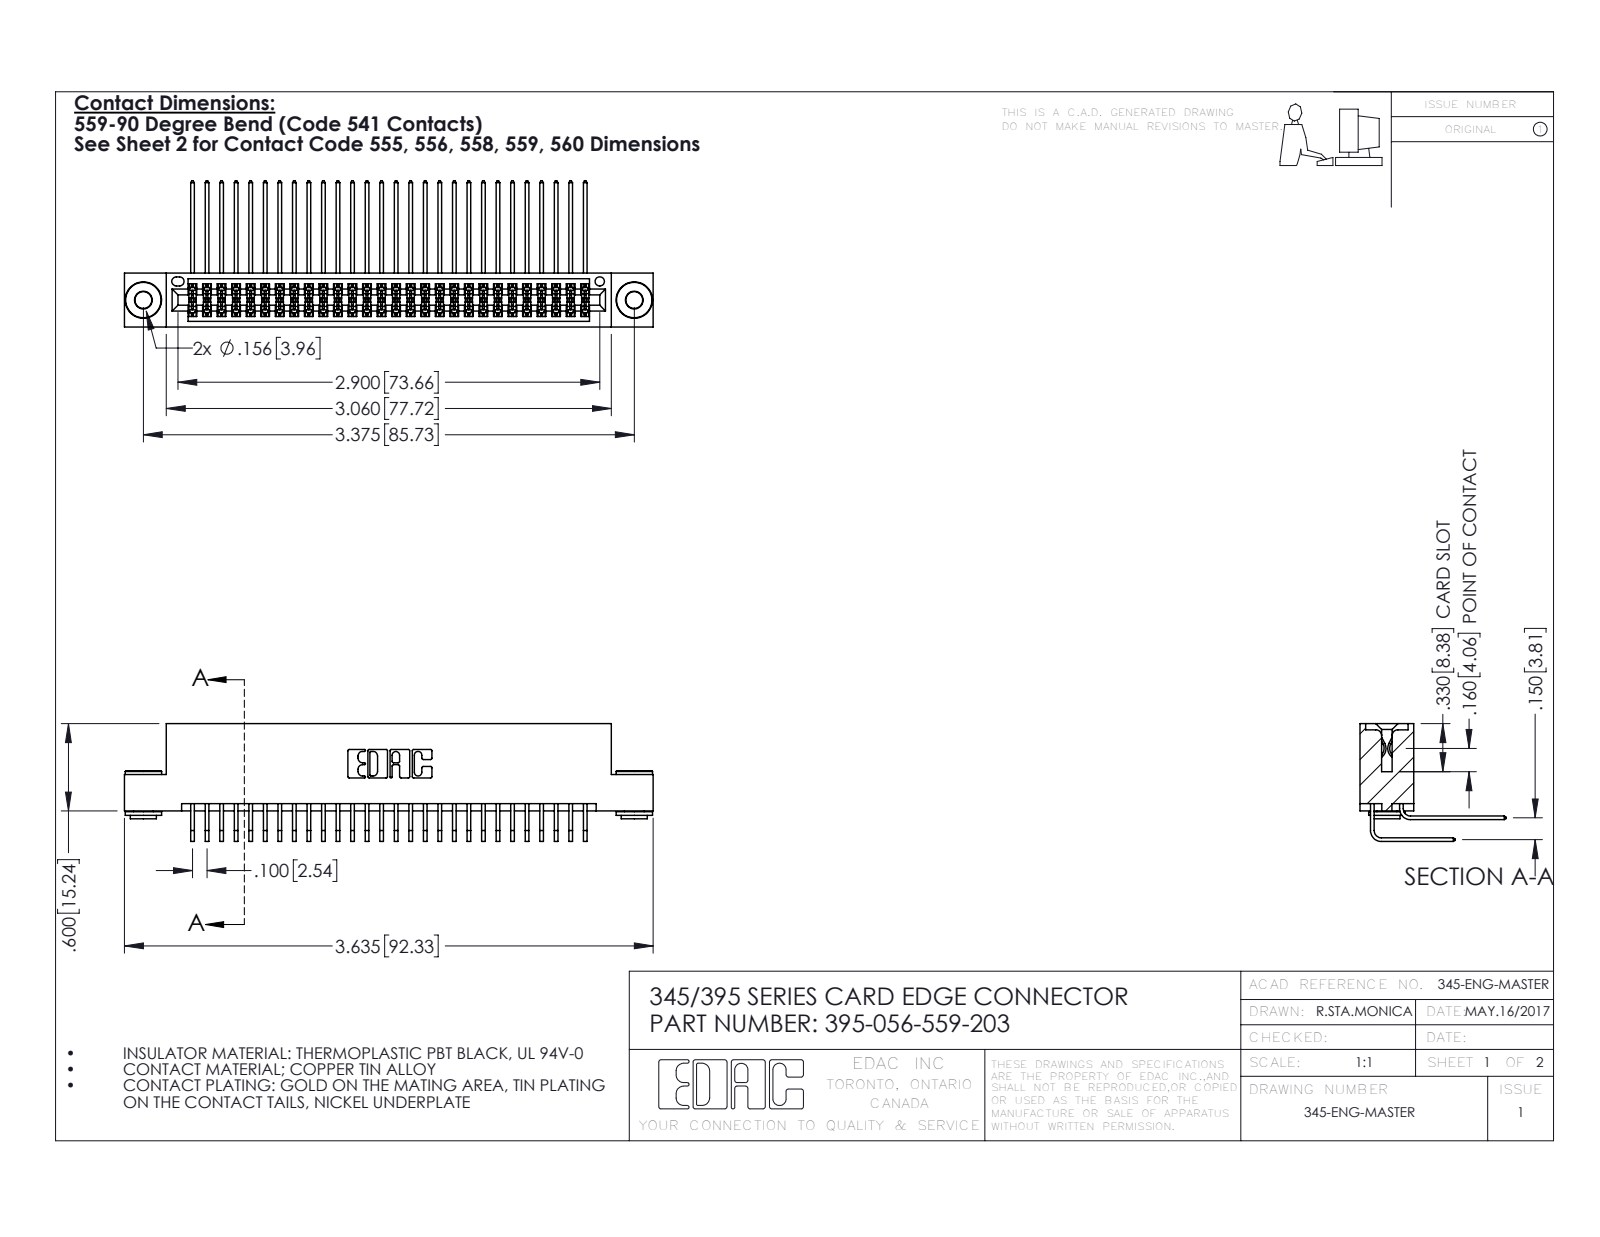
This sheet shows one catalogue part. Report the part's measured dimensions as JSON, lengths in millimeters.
{"part_name": "345-292-001_558 559 Tail - 1; 345-292-001_559 Tail - 2; 395-056-559-203; 345 Part_Flush Mounting Lugs - 0.156 Dia-TH (+1 more)", "step_written_by": "SolidWorks 2016 (CONFIG_CONTROL_DESIGN)", "units": "millimeters", "bodies": {"solids": 59, "faces": 3076, "planar": 2050, "cylindrical": 1018, "other": 8}, "overall_size": [92.3, 25.5, 20.5], "volume_mm3": 9180, "surface_area_mm2": 15030, "round_holes": [[2.9, 2], [4, 2], [1.6, 1]], "round_bosses_or_shafts": [[6.4, 2], [4.6, 2], [3.5, 2]], "partial_cylinders_radius": [[0.2, 111], [0.3, 22], [0.2, 6], [0.8, 6], [0.7, 3], [0.4, 2], [0.5, 2], [0.6, 2]], "face_to_face_distances": [1.8, 7.6, 5.1, 9.4, 0.6, 2.5, 6.9, 5.7, 3.8, 4.4], "hole_center_spacings": [6.9, 79.8, 85.7]}
